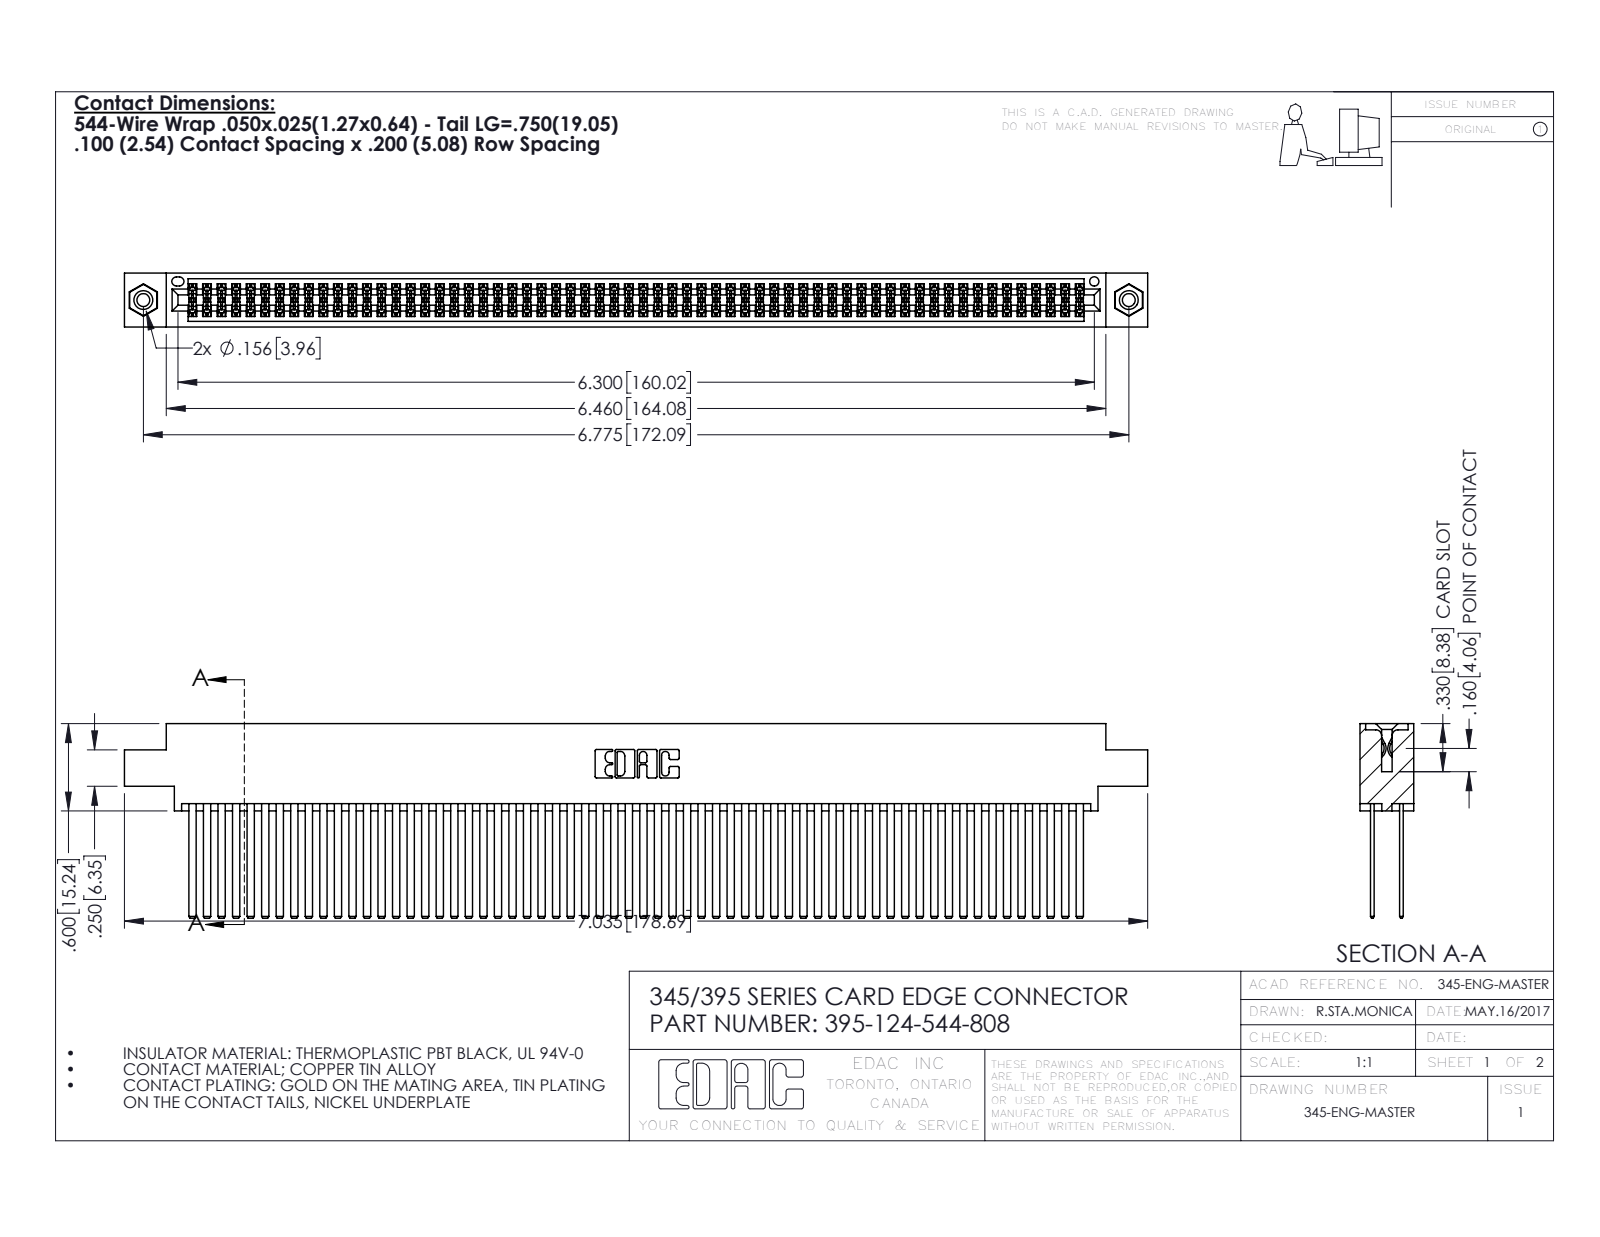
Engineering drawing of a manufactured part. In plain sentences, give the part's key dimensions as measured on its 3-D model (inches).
The part is named "345-292-001_345-293-144; 345-250-001_345-250-003-102; 345 Part_0.170 Offset - 0.156 Dia-TI; 395-124-544-808". Its 3-D file was written by "SolidWorks 2016 (CONFIG_CONTROL_DESIGN)". It is 127 solids with 5646 faces: 3712 planar, 1918 cylindrical and 16 other. Overall it measures 7.035 by 1.337 by 0.37 inches. Its volume is 1.169 cubic inches and its surface area 52.64 square inches. Round holes: 2 of diameter 0.089, 2 of diameter 0.125, 2 of diameter 0.156, 1 of diameter 0.064. Round bosses or shafts: 2 of diameter 0.155. Partial cylindrical surfaces (rounded edges, fillets, slot ends): 186 of radius 0.006, 22 of radius 0.01, 6 of radius 0.007, 6 of radius 0.031, 3 of radius 0.026, 2 of radius 0.014, 2 of radius 0.019, 2 of radius 0.022. The main face-to-face distances are 0.2, 0.025, 0.072, 0.098, 0.272, 0.298, 0.225, 0.175, 0.37, 0.15. The hole center spacings are 0.27, 6.539, 6.775.
